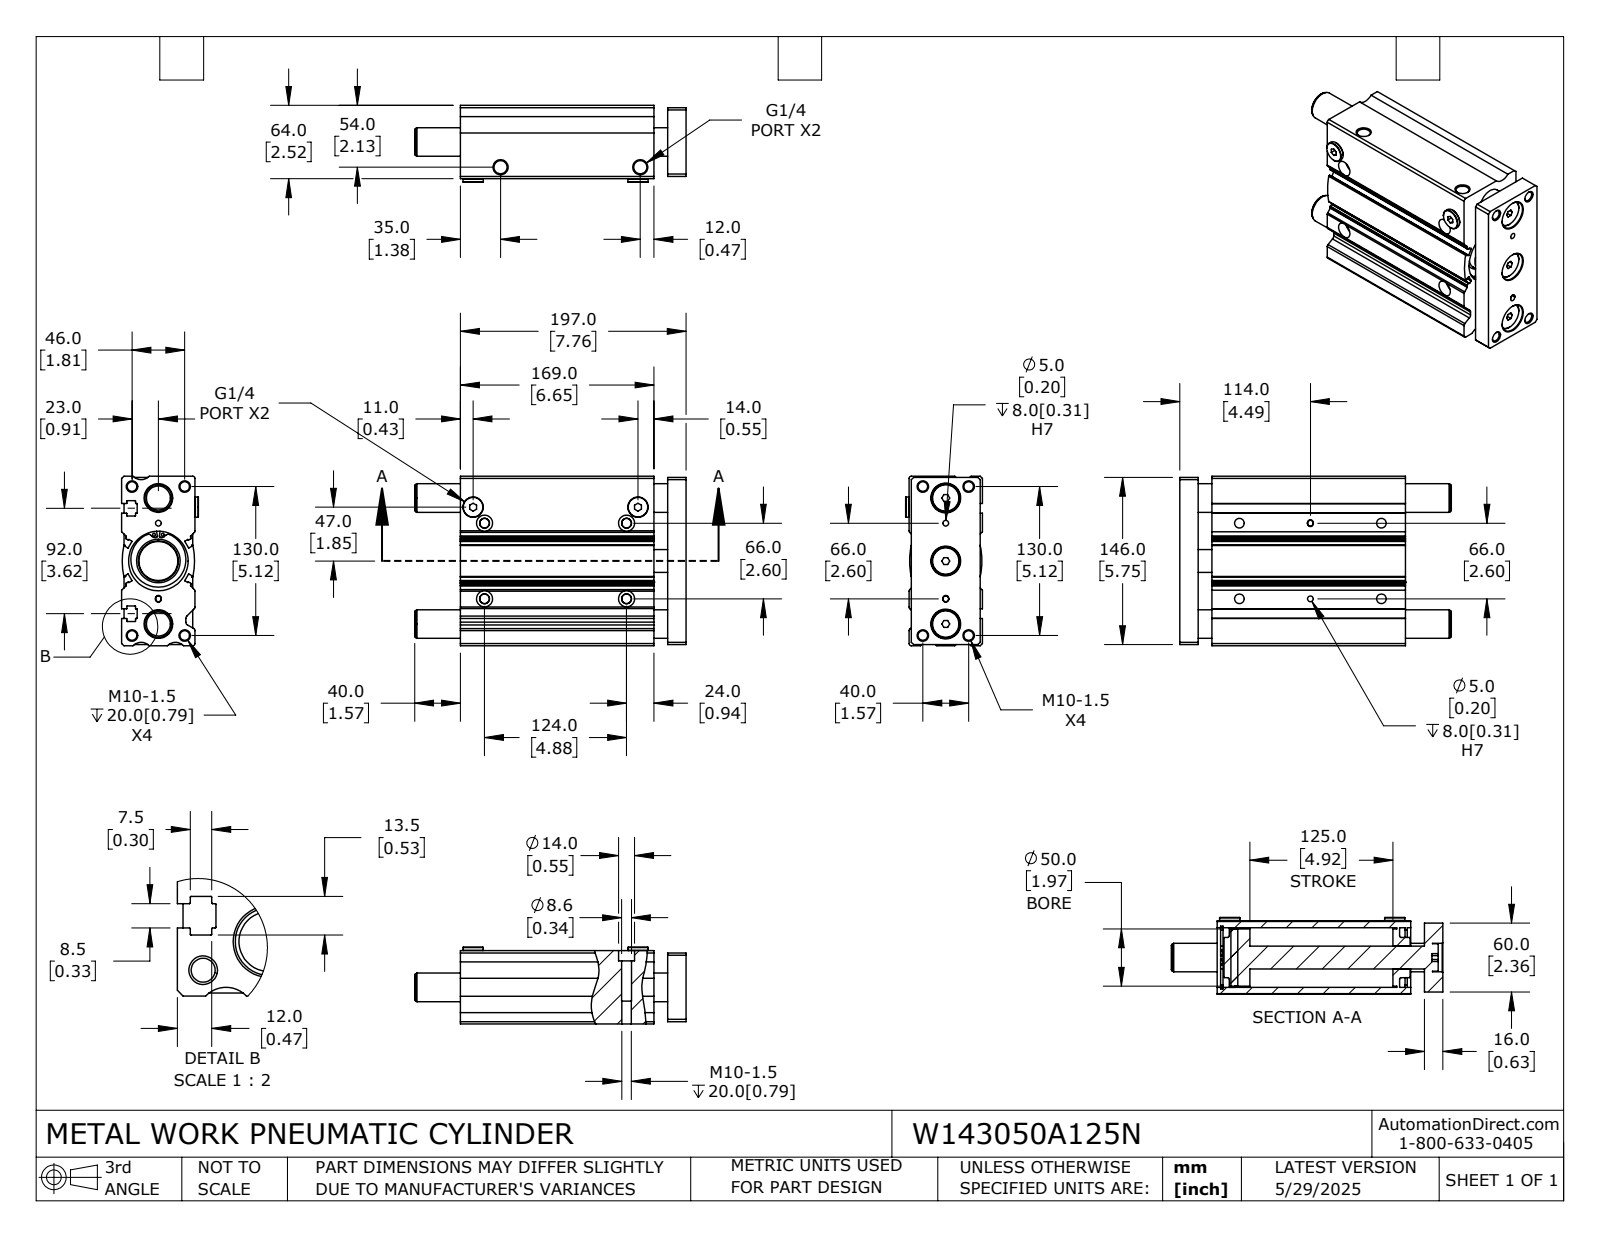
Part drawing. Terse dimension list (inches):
name: W143050A125N_BODY; W143050A125N; W143050A125N_ROD
written by: SolidWorks 2024 (CONFIG_CONTROL_DESIGN)
unit: in
bodies: 4 solids, 464 faces (186 planar, 222 cylindrical, 56 other)
size: 9.331 × 5.827 × 2.638
volume: 84.15 in³; area: 409.2 in²
holes: 12× ⌀0.33, 4× ⌀0.098, 4× ⌀0.197, 4× ⌀0.339, 4× ⌀0.551, 3× ⌀0.984, 2× ⌀0.451, 2× ⌀1.89, 1× ⌀0.787, 1× ⌀2.047
bosses: 3× ⌀0.945, 2× ⌀0.697, 1× ⌀2.165, 1× ⌀1.969, 1× ⌀1.378
rounds: 44× R0.012, 12× R0.02, 10× R0.118, 6× R0.079, 6× R2.677, 4× R0.039, 4× R0.098, 3× R0.394
face distances: 0.472, 2.52, 6.654, 0.63, 7.126, 5.827, 0.079, 1.102, 7.756, 0.098
hole spacings: 0.118, 0.424, 0.869, 0.88, 0.916, 0.963, 0.987, 1.271
